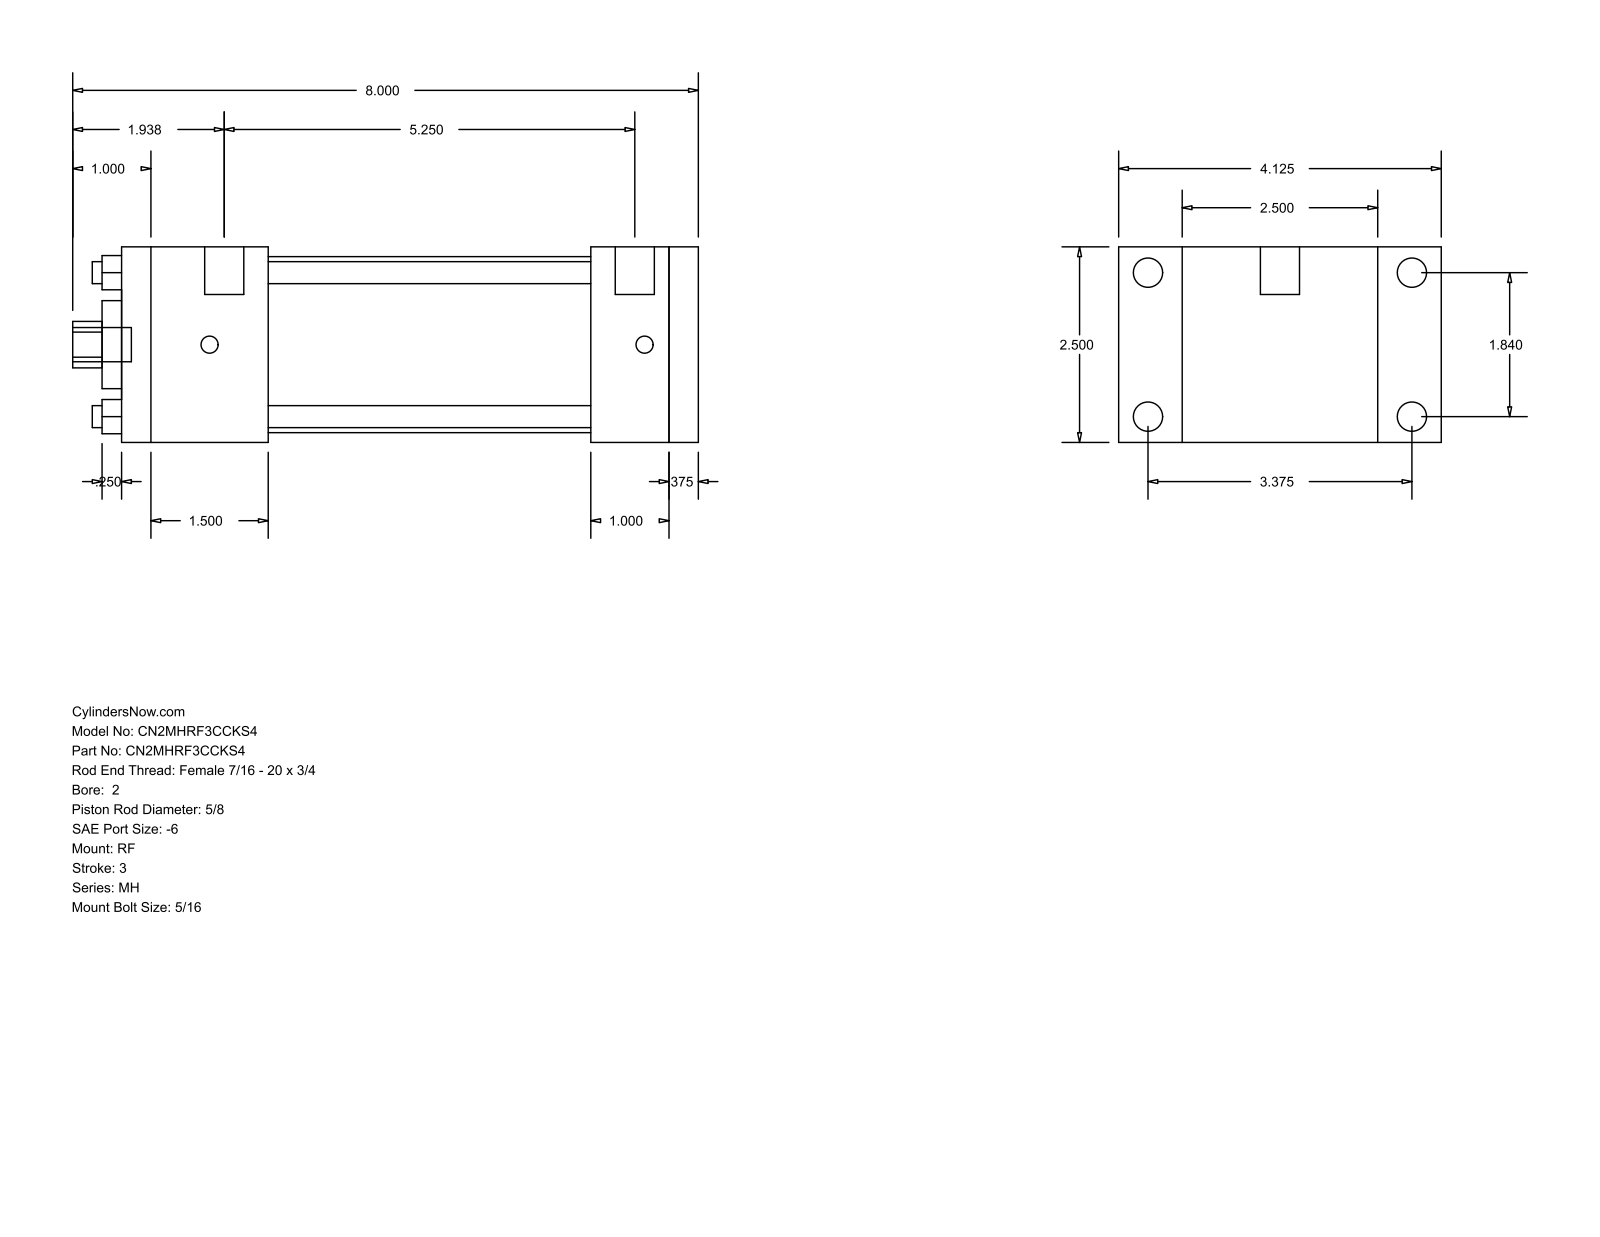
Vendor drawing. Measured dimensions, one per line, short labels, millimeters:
name: MH_RF__0200_0.625
written by: GSSL Pune (CONFIG_CONTROL_DESIGN)
unit: mm
bodies: 0 solids, 92 faces (64 planar, 28 cylindrical, 0 other)
size: 203.2 × 104.78 × 63.5
holes: 4× ⌀7.14, 1× ⌀15.88, 1× ⌀28.57, 1× ⌀57.15
bosses: 4× ⌀9.53, 4× ⌀5.56, 2× ⌀12.7, 1× ⌀11.11
rounds: 1× R7.54
face distances: 63.5, 187.32, 9.52, 177.8, 104.78, 25.4, 47.62, 152.4, 130.18, 139.7
hole spacings: 33.05, 46.74, 66.1
